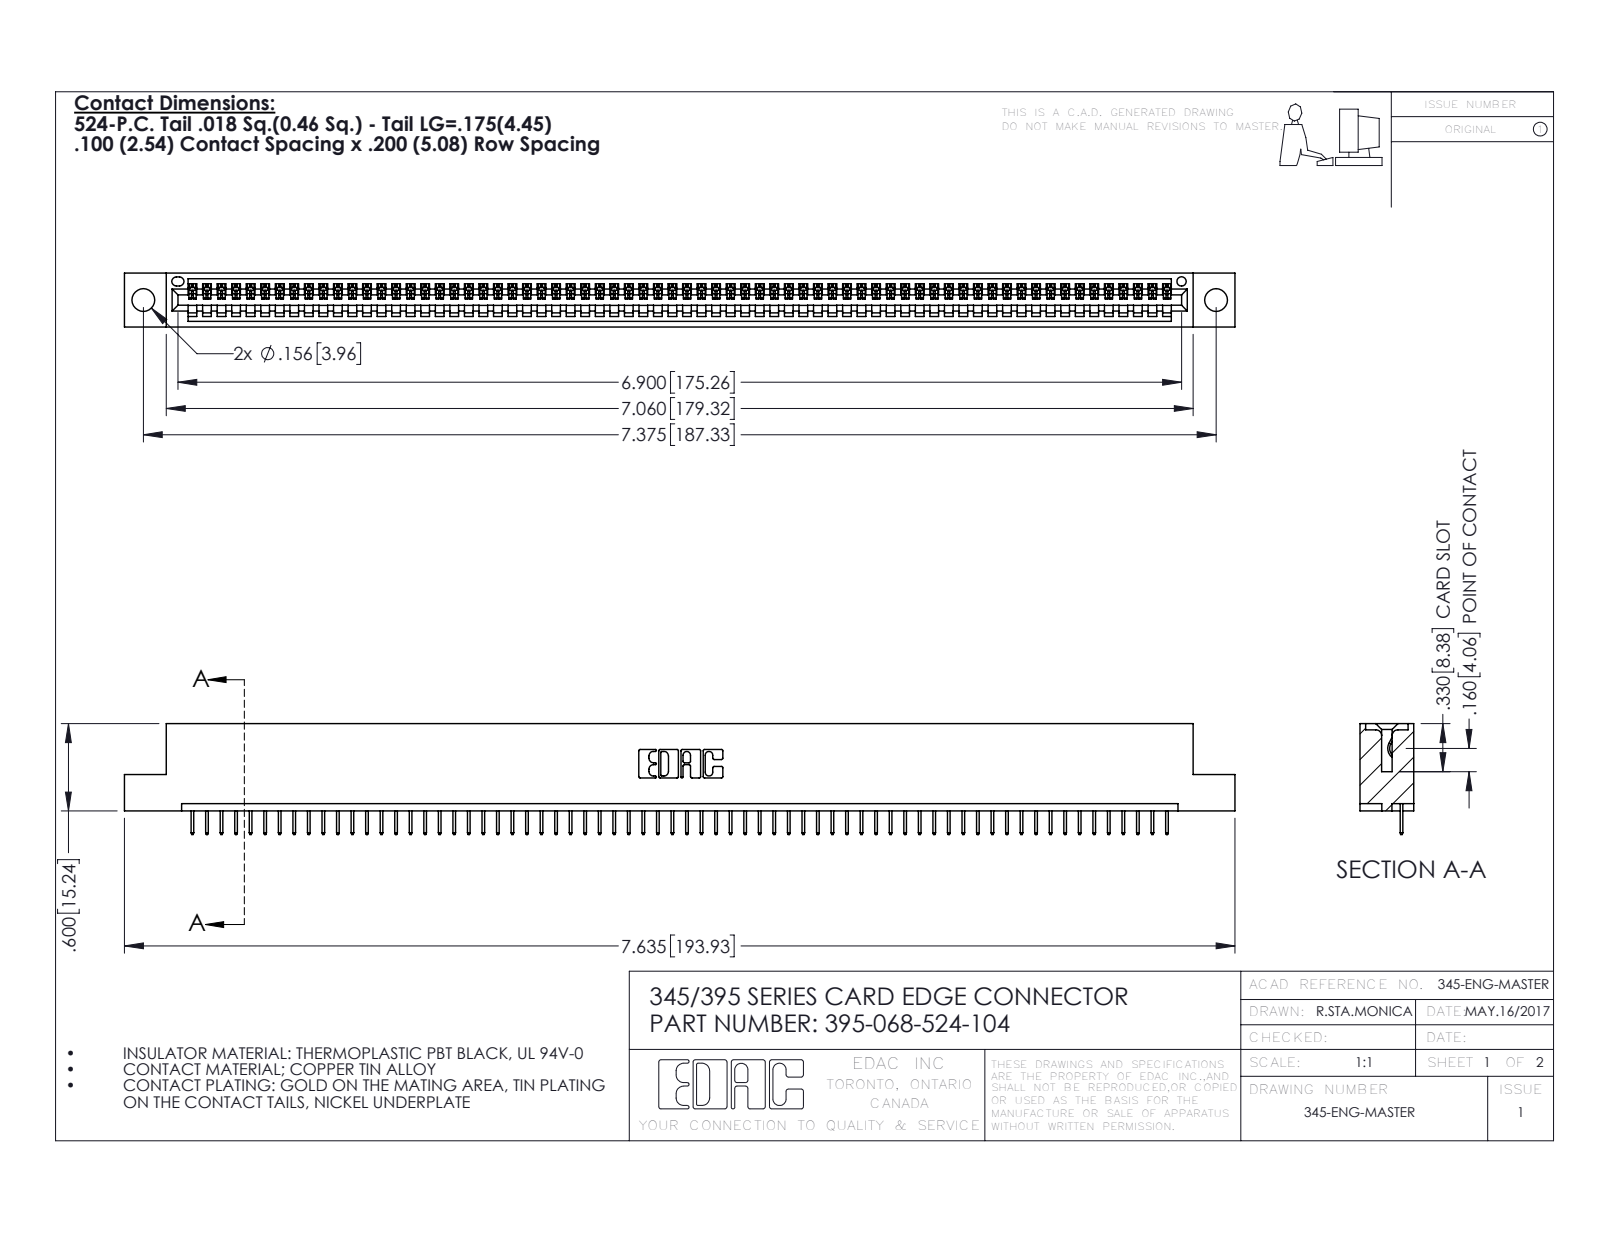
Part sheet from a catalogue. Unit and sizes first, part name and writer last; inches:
Units: inches
Overall size (bounding box): 7.635 × 0.762 × 0.37
Round holes (diameter × count): ⌀0.156 ×2, ⌀0.064 ×1
Partial cylindrical surfaces — rounded edges, fillets, slot ends (radius × count): R0.006 ×136, R0.01 ×22, R0.007 ×6, R0.031 ×6, R0.026 ×3, R0.031 ×2, R0.04 ×2, R0.014 ×1
Main face-to-face distances: 0.298, 0.072, 0.37, 0.2, 0.098, 0.272, 0.025, 0.225, 0.072, 0.149
Hole centre spacings: 0.27, 7.139, 7.375
Volume: 1.115 in³ · Surface area: 36.57 in²
Bodies: 69 solids, 4342 faces (3208 planar, 1134 cylindrical, 0 other)
Part name (STEP PRODUCT): 395-068-524-104; 345 Part_Flush Mounting Lugs - 0.156 Dia-TH; 345-292-001_345-293-124
STEP written by: SolidWorks 2016 (CONFIG_CONTROL_DESIGN)
